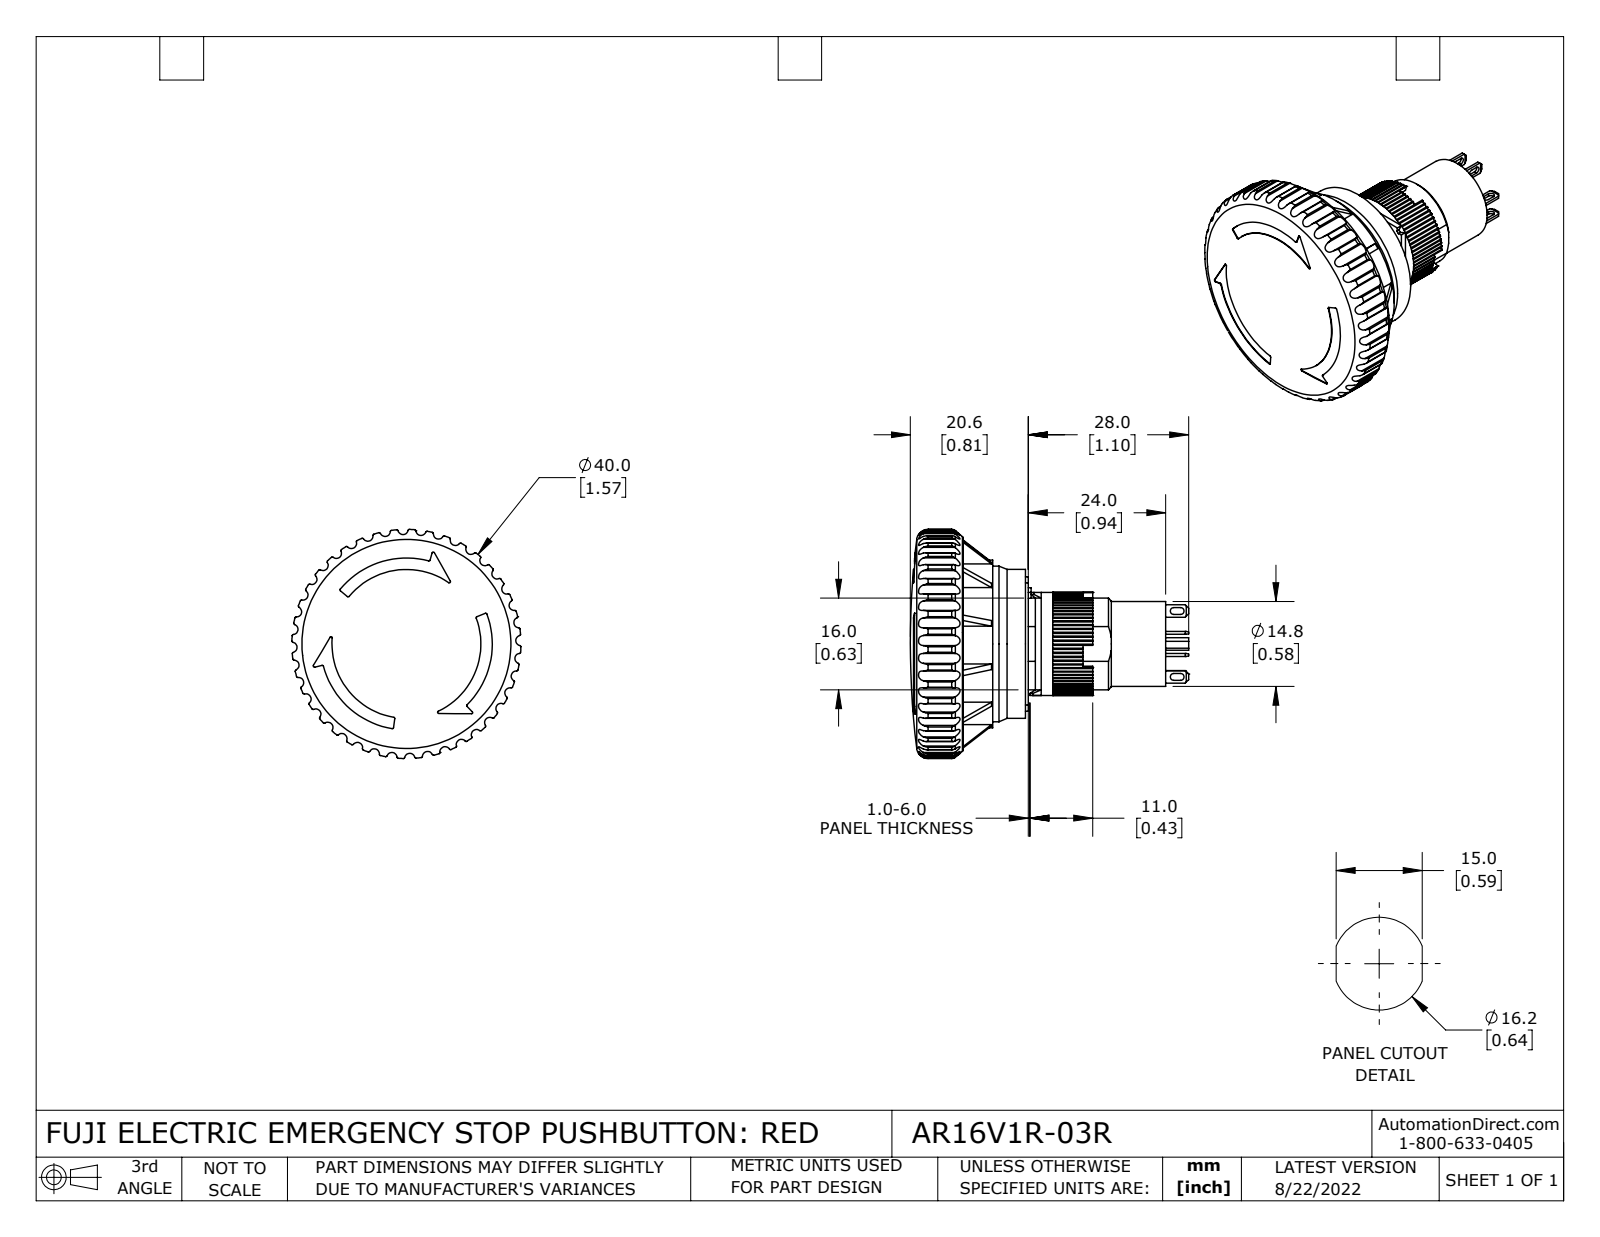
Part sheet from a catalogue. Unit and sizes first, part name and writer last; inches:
Units: inches
Overall size (bounding box): 1.913 × 1.575 × 1.575
Round holes (diameter × count): ⌀0.583 ×1, ⌀0.63 ×1, ⌀0.709 ×1, ⌀1.069 ×1, ⌀1.433 ×1
Round bosses / shafts (diameter × count): ⌀1.154 ×1, ⌀1.024 ×1, ⌀0.858 ×1, ⌀0.236 ×1
Partial cylindrical surfaces — rounded edges, fillets, slot ends (radius × count): R0.008 ×80, R0.01 ×80, R0.035 ×40, R0.02 ×8, R0.024 ×8, R0.039 ×2, R0.031 ×1, R0.114 ×1
Main face-to-face distances: 0.039, 0.421, 0.53, 0.108, 0.02, 0.069, 0.856, 0.49, 0.089, 0.049
Volume: 0.963 in³ · Surface area: 19.04 in²
Bodies: 5 solids, 1001 faces (495 planar, 410 cylindrical, 96 other)
Part name (STEP PRODUCT): AR16V1R-03R
STEP written by: SolidWorks 2021 (CONFIG_CONTROL_DESIGN)
